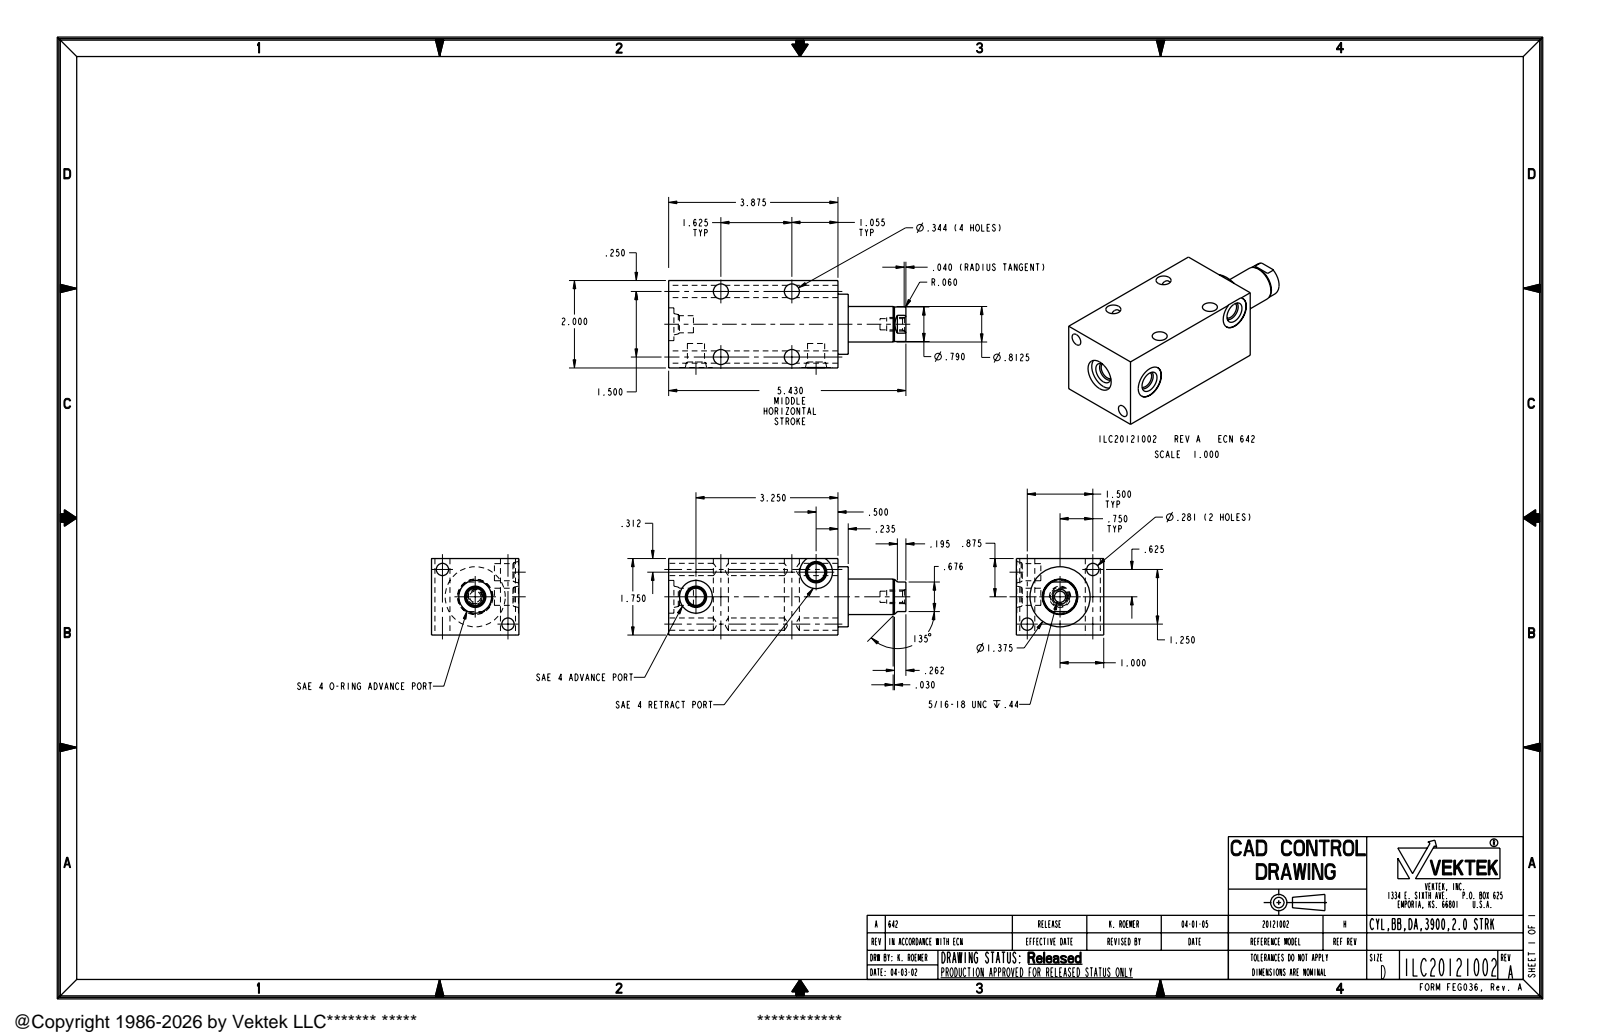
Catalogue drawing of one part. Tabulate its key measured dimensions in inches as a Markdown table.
| quantity | value |
| --- | --- |
| part name | ILC20121002 |
| STEP written by | PRO/ENGINEER BY PARAMETRIC TECHNOLOGY CORPORATION, 2004290 (AUTOMOTIVE_DESIGN_CC2) |
| units | inches |
| bodies | 1 solid, 79 faces (20 planar, 41 cylindrical, 18 other) |
| overall size | 5.43 × 2 × 1.75 |
| volume | 13.23 in³ |
| surface area | 55.29 in² |
| round holes (diameter × count) | 0.344 × 4, 0.392 × 3, 0.75 × 3, 0.281 × 2, 0.257 × 1 |
| round bosses / shafts (diameter × count) | 1.375 × 1, 0.813 × 1, 0.79 × 1, 0.312 × 1 |
| main face-to-face distances | 1.75, 2, 3.875, 0.235, 4.11, 1.99, 1.32, 1.555, 5.43, 5.31 |
| hole center spacings | 0.976, 1.5, 1.625, 2.211, 1.953, 2.807 |
